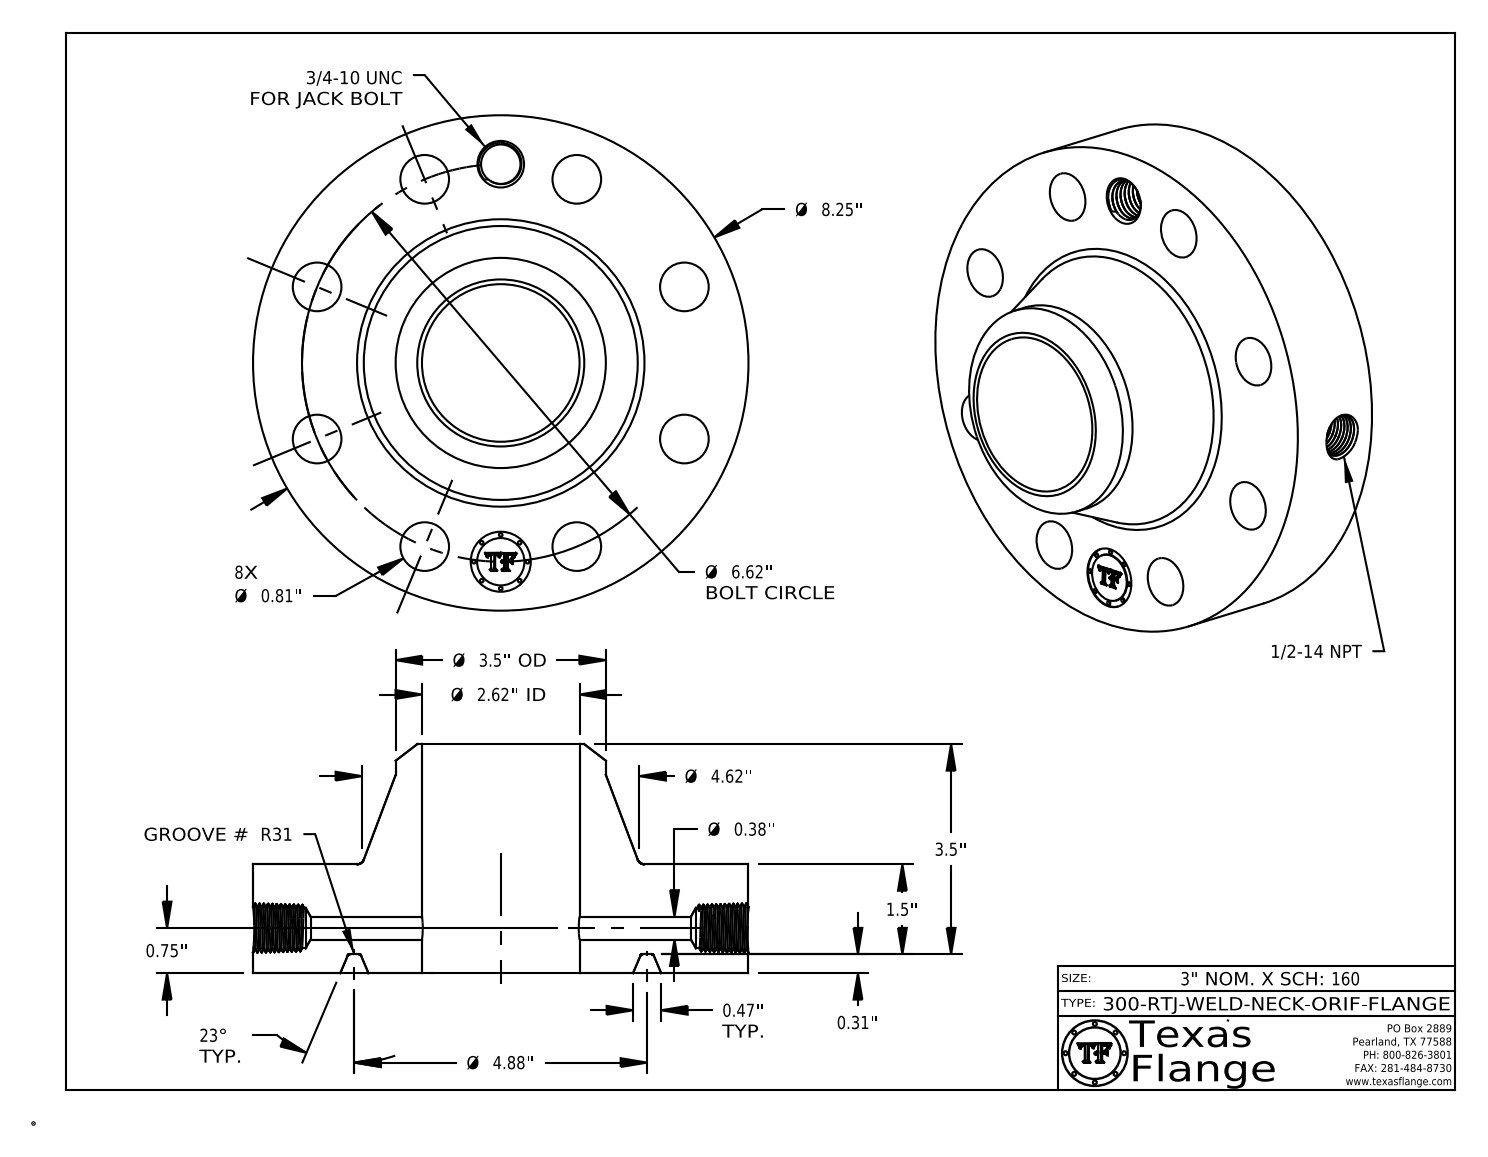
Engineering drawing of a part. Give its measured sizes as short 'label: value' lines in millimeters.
name: 300-RTJ-WELD-NECK
written by: CATIA V5 STEP AP214 (AUTOMOTIVE_DESIGN)
unit: mm
bodies: 1 solid, 795 faces (370 planar, 96 cylindrical, 329 other)
size: 209.6 × 209.6 × 96.9
volume: 1 461 000 mm³; area: 155 900 mm²
holes: 8× ⌀20.6, 1× ⌀9.7, 1× ⌀16.7, 1× ⌀17.1, 1× ⌀25.4, 1× ⌀66.6
bosses: 8× ⌀1.5, 1× ⌀209.6, 1× ⌀88.9, 1× ⌀20
face distances: 46.1, 8, 38.1, 96.9, 88.9, 50.8, 0.4, 45.7, 37.7, 51.2
hole spacings: 84.1, 118.9, 155.3, 168.1, 32.8, 64.3, 64.3, 93.4
